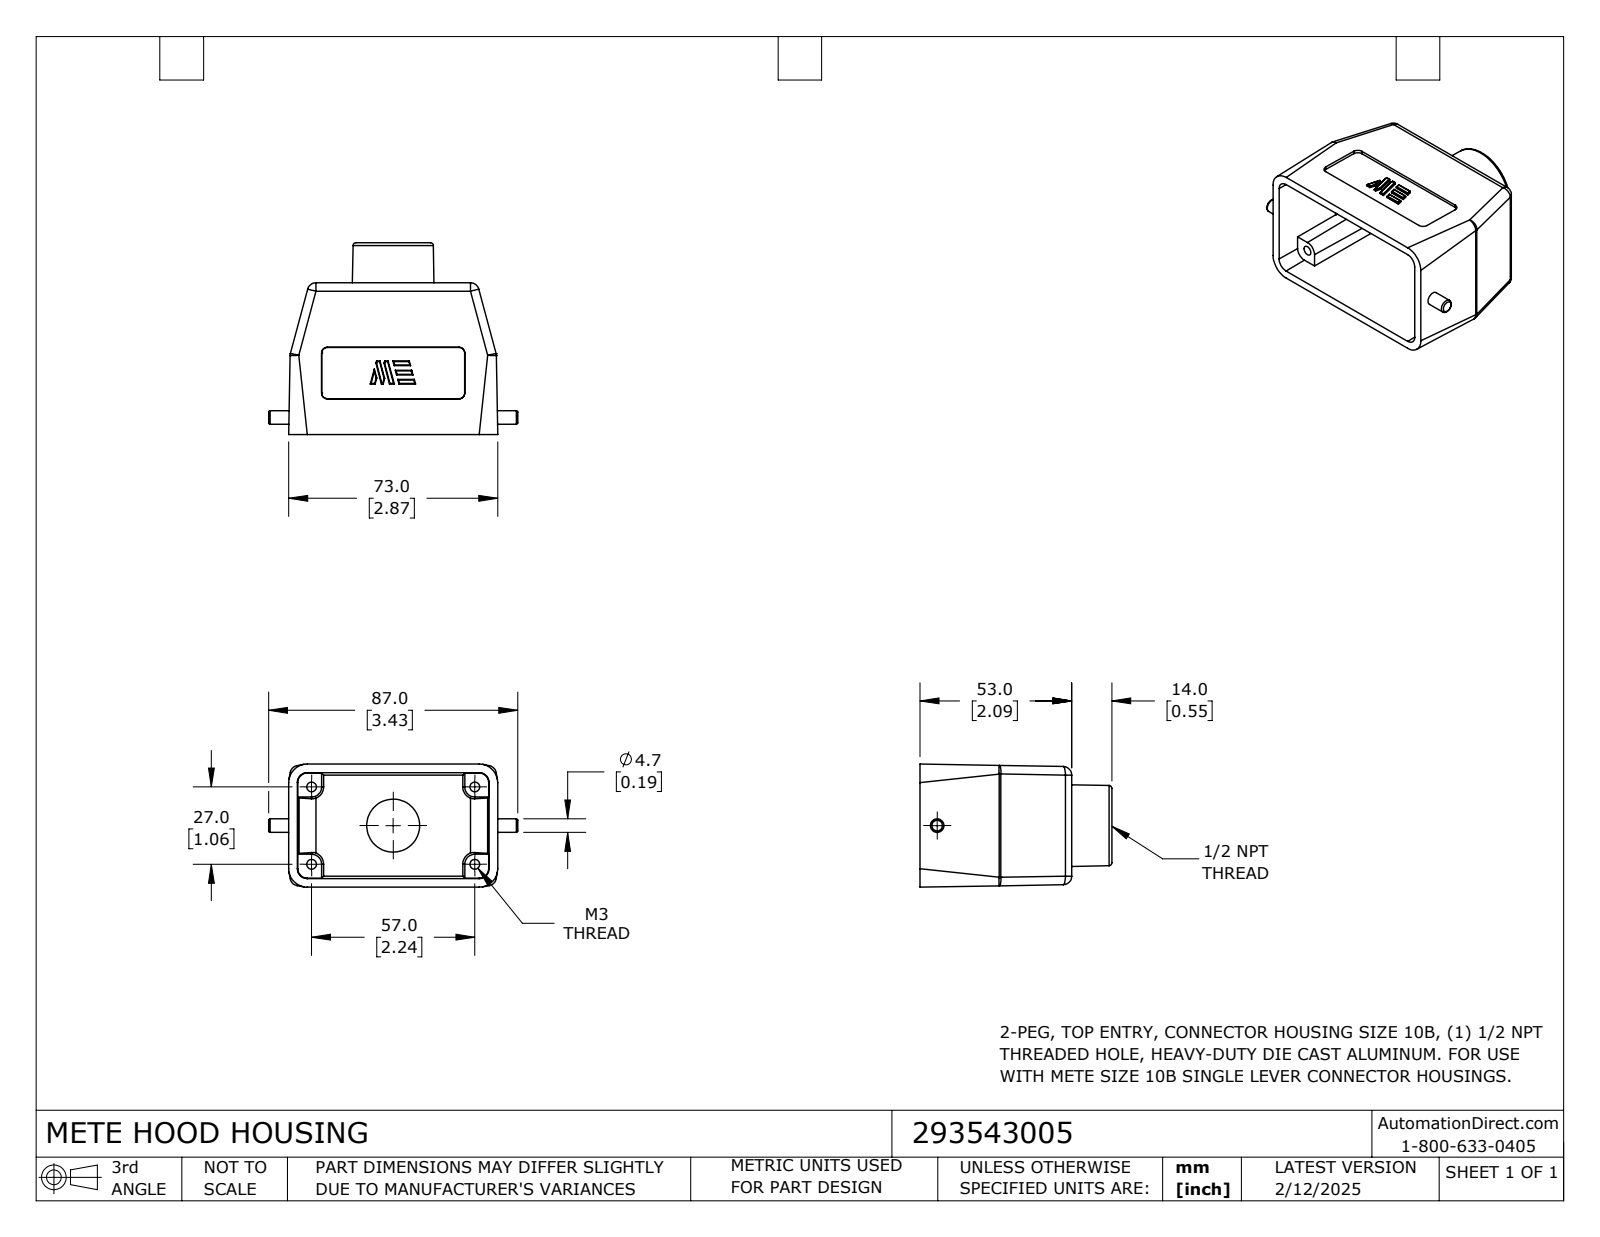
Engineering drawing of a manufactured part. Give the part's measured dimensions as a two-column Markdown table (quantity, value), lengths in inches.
| quantity | value |
| --- | --- |
| part name | 293543005 |
| STEP written by | SolidWorks 2024 (CONFIG_CONTROL_DESIGN) |
| units | inches |
| bodies | 1 solid, 233 faces (111 planar, 88 cylindrical, 34 other) |
| overall size | 3.425 × 2.638 × 1.693 |
| volume | 2.963 in³ |
| surface area | 44.27 in² |
| round holes (diameter × count) | 0.134 × 4, 0.728 × 1 |
| round bosses / shafts (diameter × count) | 0.185 × 1 |
| partial cylindrical surfaces (radius × count) | 0.008 × 35, 0.079 × 8, 0.118 × 8, 0.039 × 2, 0.098 × 2 |
| main face-to-face distances | 0.118, 0.04, 0.078, 0.447, 0.329, 1.969, 2.087, 0.407, 0.354, 1.614 |
| hole center spacings | 1.242, 1.063, 2.244, 2.483 |
